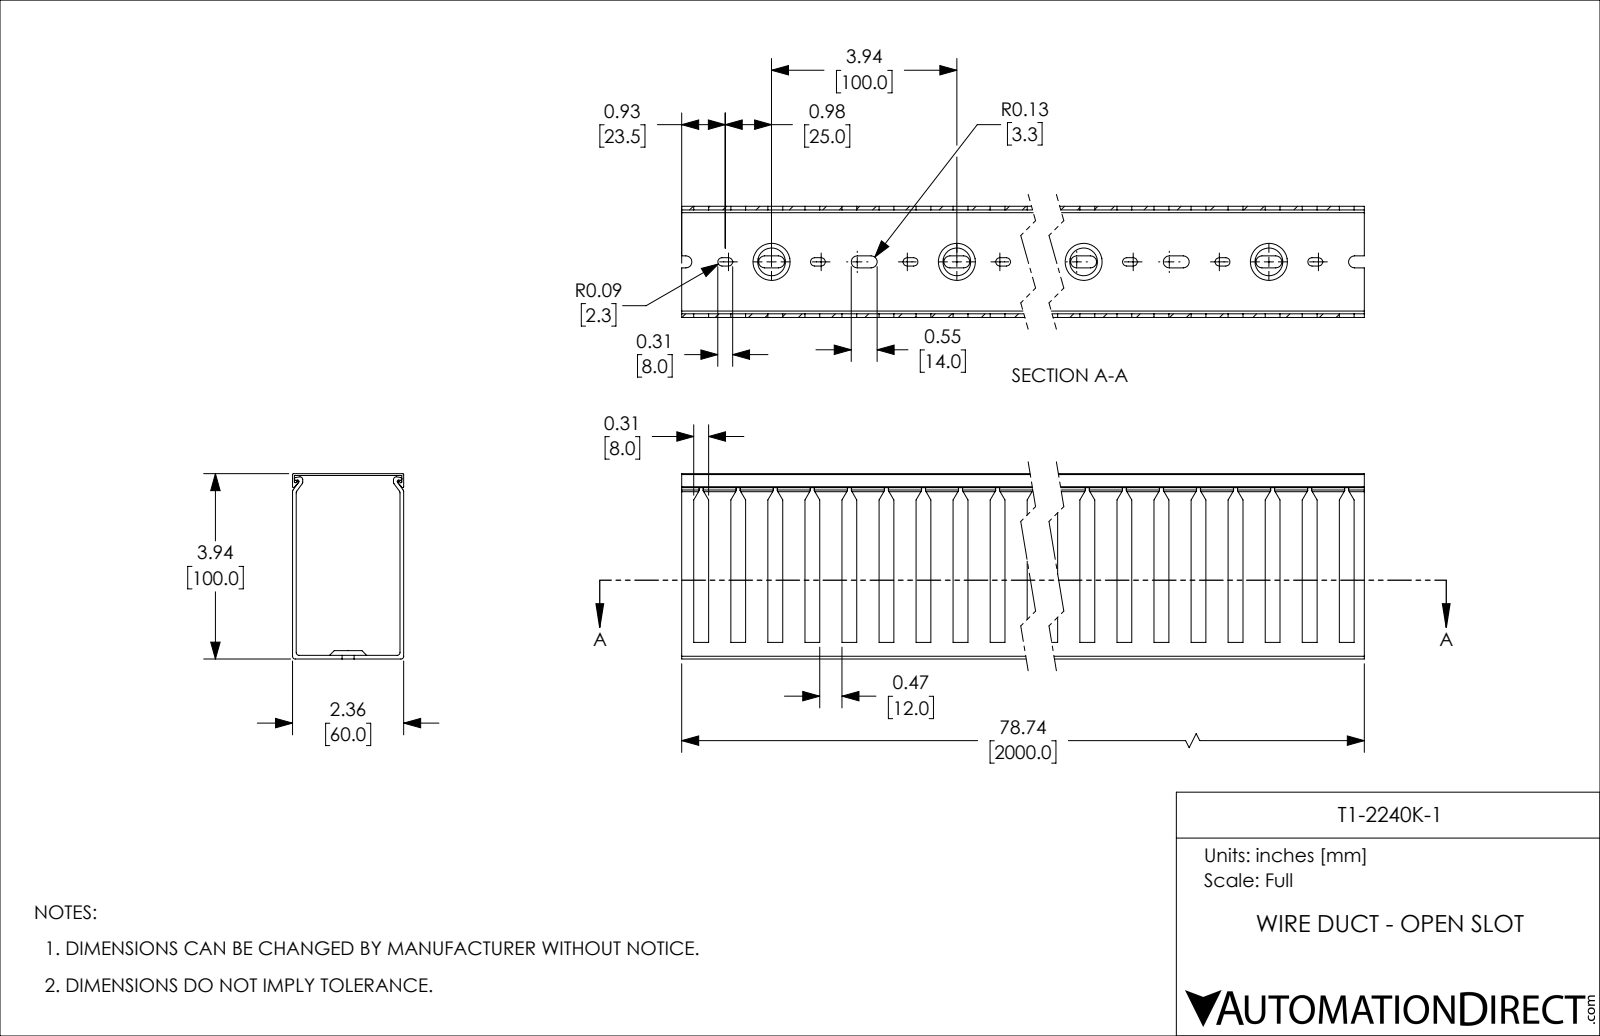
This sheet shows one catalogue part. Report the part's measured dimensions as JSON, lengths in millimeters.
{"part_name": "T1-2240K-1", "step_written_by": "SolidWorks 2021 (CONFIG_CONTROL_DESIGN)", "units": "millimeters", "bodies": {"solids": 2, "faces": 1005, "planar": 534, "cylindrical": 431, "other": 40}, "overall_size": [2000, 100, 60], "volume_mm3": 1162000, "surface_area_mm2": 1322000, "partial_cylinders_radius": [[2.25, 80], [3.25, 80], [1.5, 12], [0.5, 8], [0.75, 6]], "face_to_face_distances": [2, 58, 60, 56, 1, 100, 99, 97, 98, 59]}
